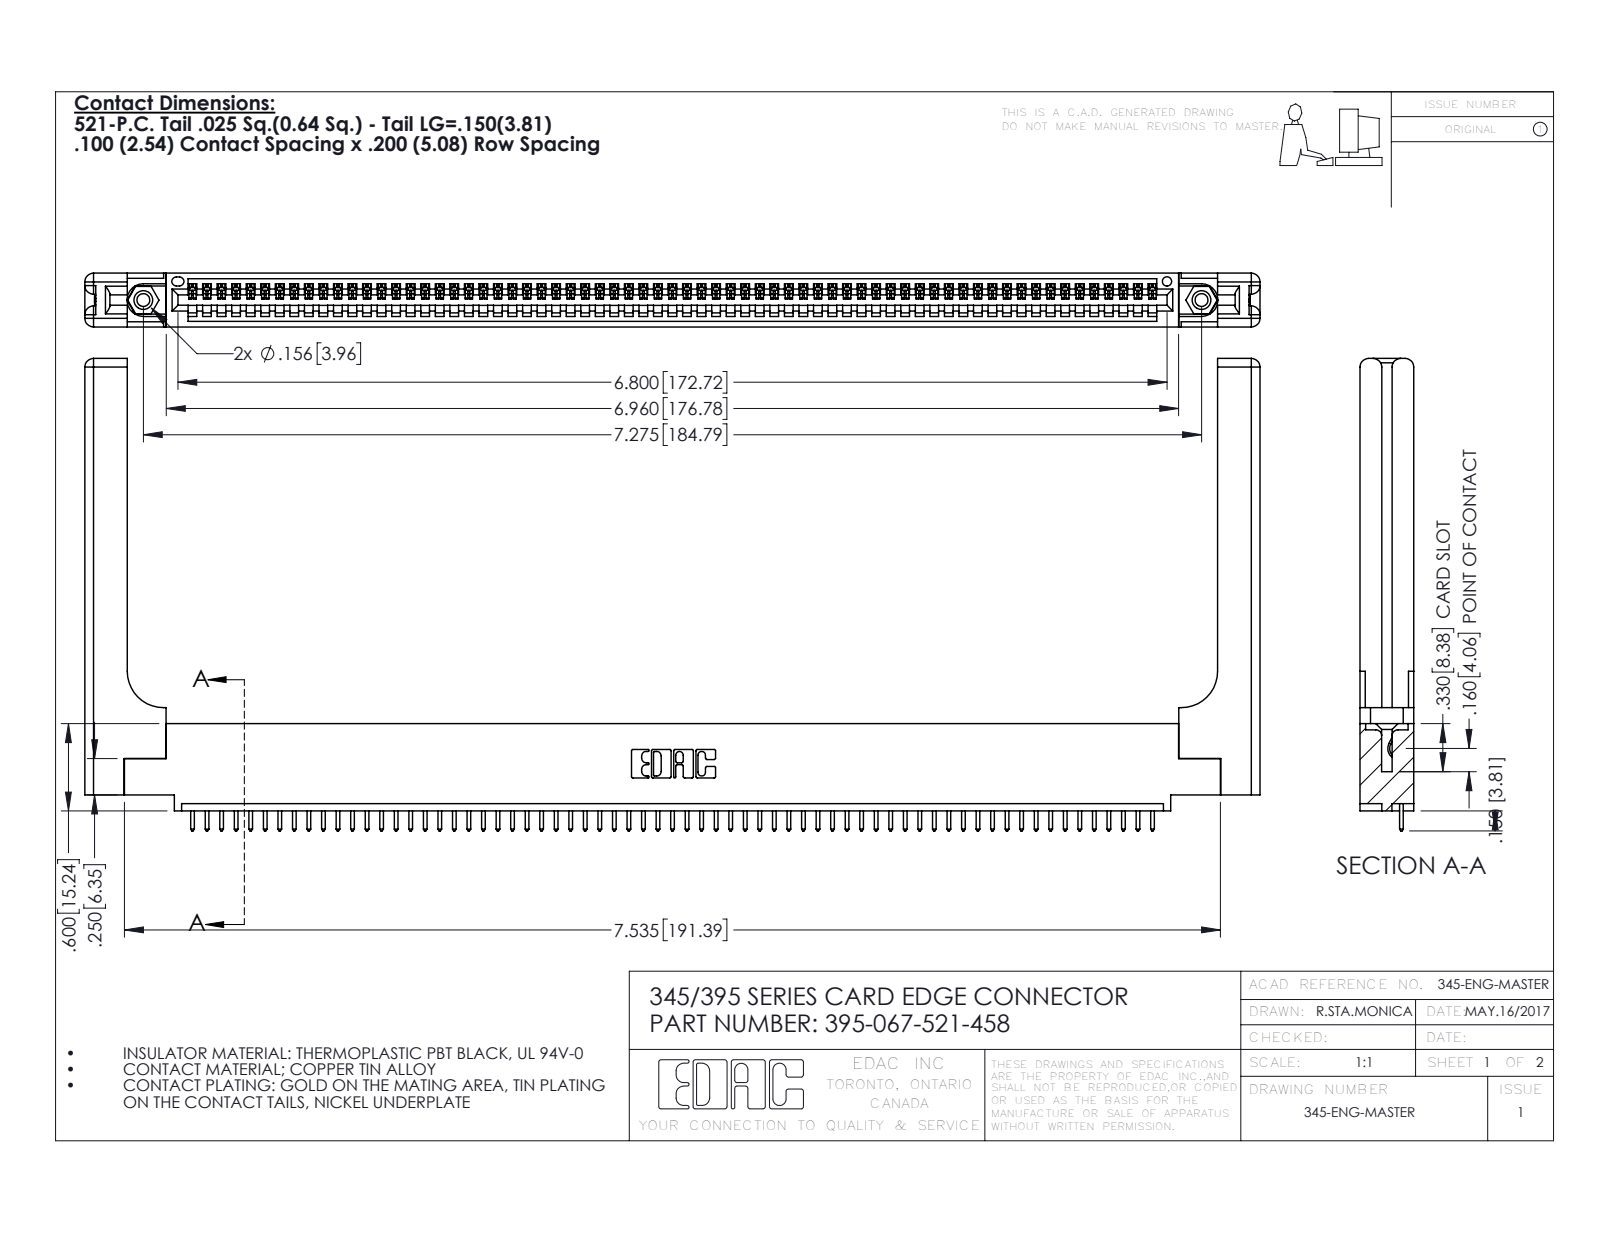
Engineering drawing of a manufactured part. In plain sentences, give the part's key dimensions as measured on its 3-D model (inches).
The part is named "345 Part_0.110 Offset - 0.156 Dia-TH; 345-220-058_345-220-058; 345-250-001_345-250-001-102; 395-067-521-458 (+1 more)". Its 3-D file was written by "SolidWorks 2016 (CONFIG_CONTROL_DESIGN)". It is 72 solids with 4272 faces: 2912 planar, 1300 cylindrical and 60 other. Overall it measures 8.079 by 3.247 by 0.37 inches. Its volume is 1.705 cubic inches and its surface area 47.75 square inches. Round holes: 2 of diameter 0.089, 2 of diameter 0.125, 2 of diameter 0.156, 1 of diameter 0.064. Round bosses or shafts: 2 of diameter 0.155. Partial cylindrical surfaces (rounded edges, fillets, slot ends): 134 of radius 0.006, 134 of radius 0.01, 22 of radius 0.01, 16 of radius 0.06, 6 of radius 0.007, 6 of radius 0.031, 3 of radius 0.026, 2 of radius 0.03. The main face-to-face distances are 0.072, 0.37, 0.298, 0.098, 0.272, 0.025, 0.2, 0.225, 0.148, 0.15. The hole center spacings are 0.27, 7.039, 7.275.
